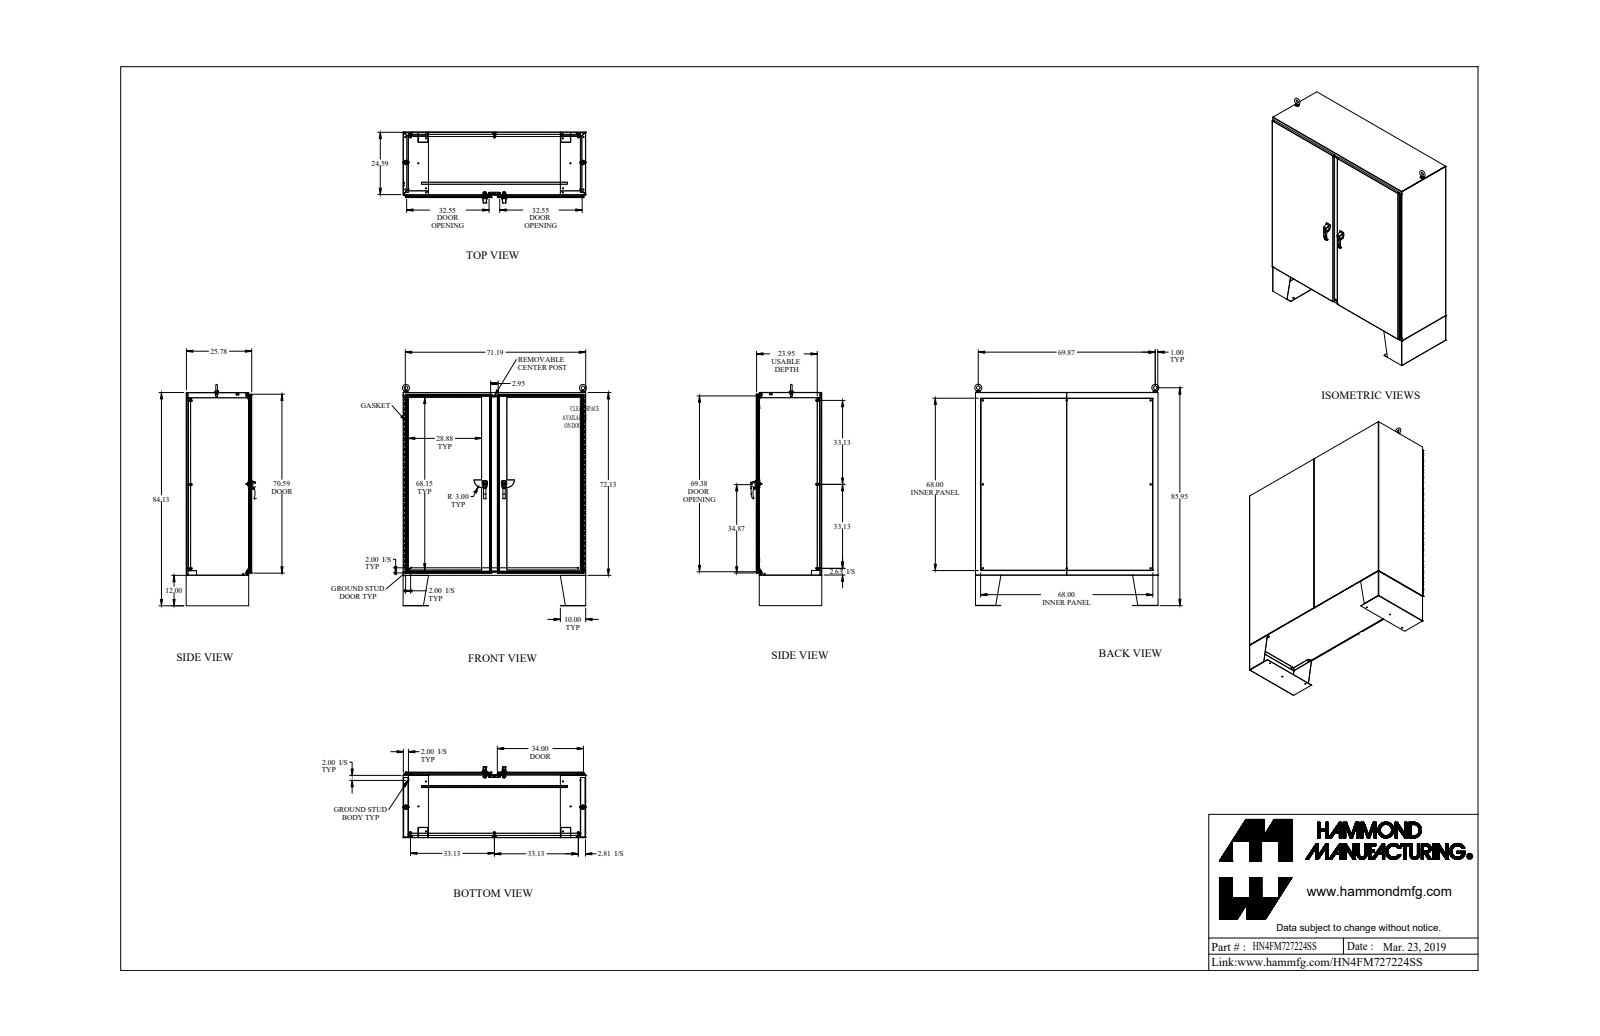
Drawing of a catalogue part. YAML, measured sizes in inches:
part_name: "HN4FM727224SS"
step_written_by: "SolidWorks 2018 (AUTOMOTIVE_DESIGN)"
units: inches
bodies: {solids: 131, faces: 3998, planar: 1834, cylindrical: 1803, other: 361}
overall_size: [87.321, 72.607, 27.99]
volume: 2753
surface_area: 55255
round_holes:
  - {diameter: 0.304, count: 24}
  - {diameter: 0.437, count: 14}
  - {diameter: 0.307, count: 8}
  - {diameter: 0.35, count: 8}
  - {diameter: 0.563, count: 8}
  - {diameter: 0.25, count: 6}
  - {diameter: 0.445, count: 6}
  - {diameter: 0.281, count: 4}
  - {diameter: 0.313, count: 4}
  - {diameter: 0.39, count: 4}
  - {diameter: 0.201, count: 3}
  - {diameter: 0.313, count: 3}
round_bosses_or_shafts:
  - {diameter: 1, count: 10}
  - {diameter: 0.65, count: 8}
  - {diameter: 0.375, count: 8}
  - {diameter: 0.332, count: 8}
  - {diameter: 0.75, count: 4}
  - {diameter: 0.625, count: 4}
  - {diameter: 0.44, count: 4}
  - {diameter: 0.37, count: 4}
partial_cylinders:
  - {radius: 0.5, count: 33}
  - {radius: 0.018, count: 32}
  - {radius: 0.125, count: 32}
  - {radius: 0.048, count: 29}
  - {radius: 0.143, count: 29}
  - {radius: 0.06, count: 28}
  - {radius: 0.03, count: 12}
  - {radius: 0.09, count: 12}
face_to_face_distances: [0.095, 25.78, 25.685, 0.125, 23.998, 25.875, 1.782, 1.687, 24.093, 1.657]
hole_center_spacings: [6, 12, 18, 24, 74.07, 30, 36, 66.25]
